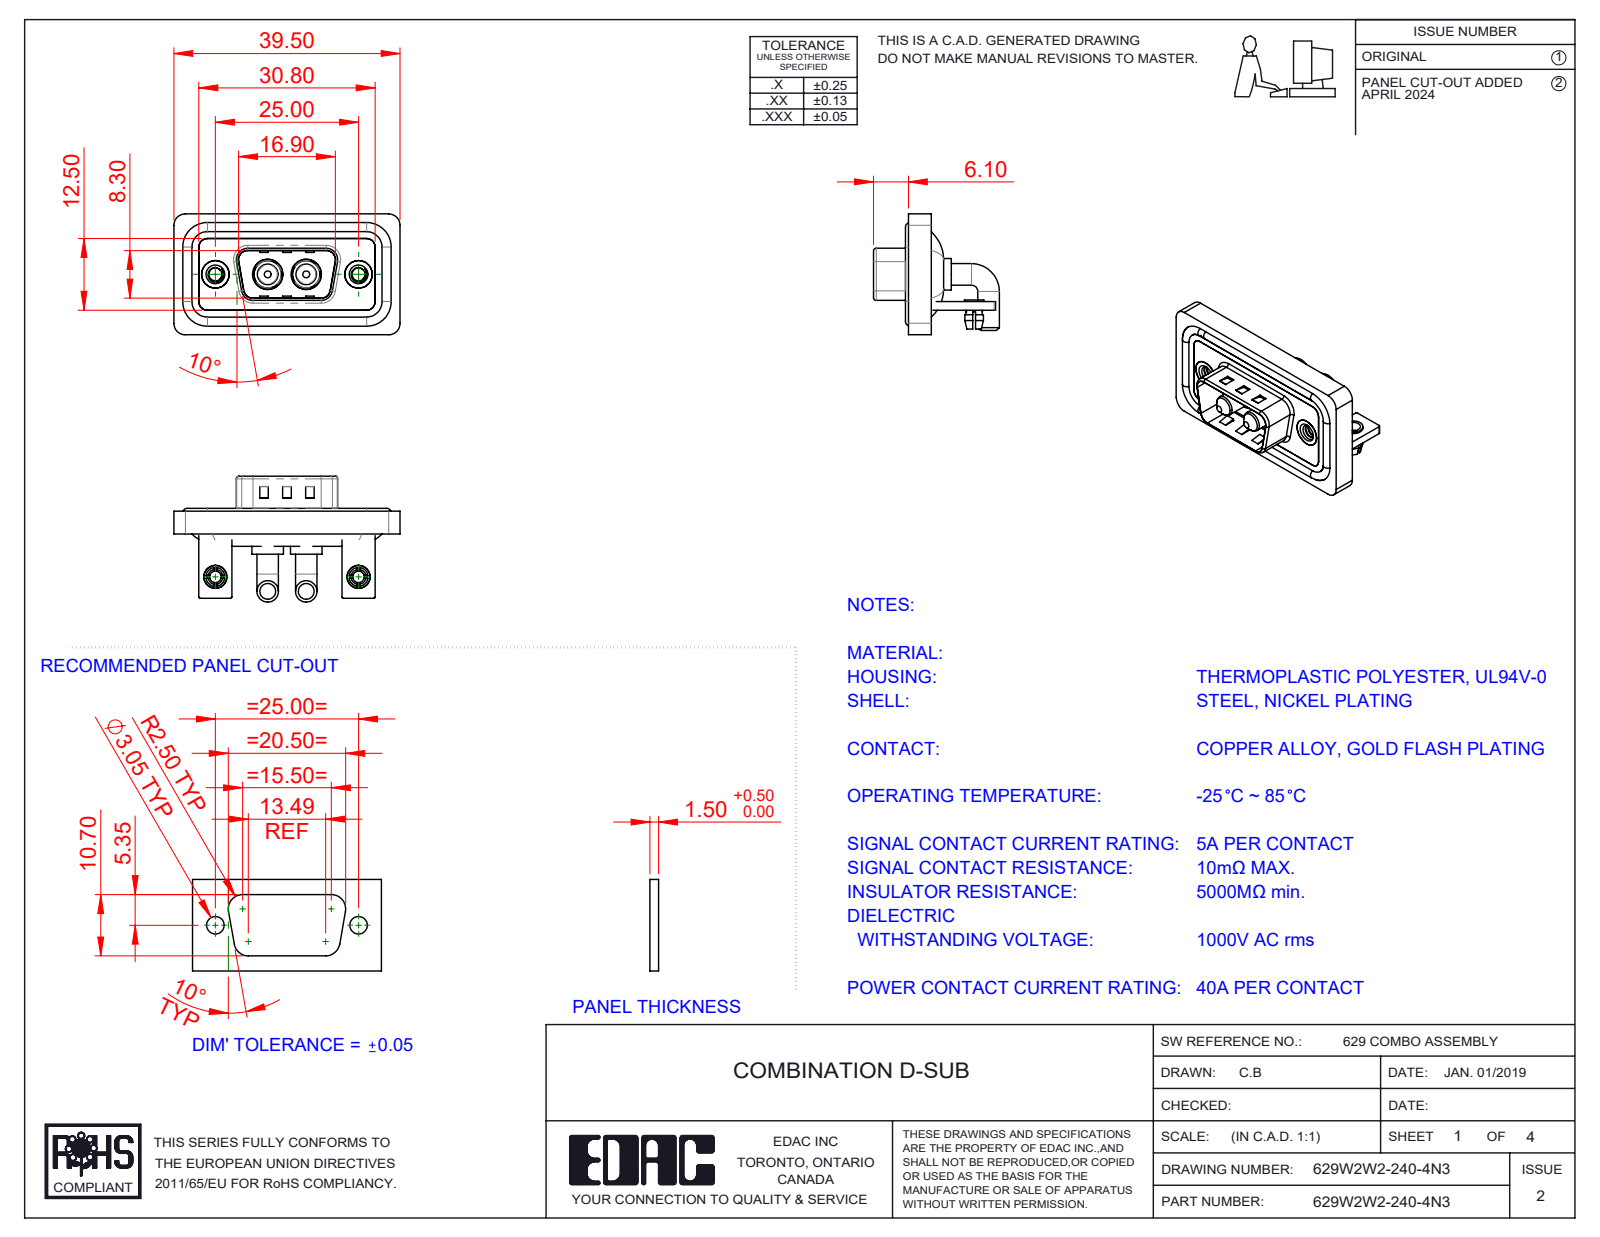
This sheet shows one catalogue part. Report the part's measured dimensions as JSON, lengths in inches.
{"part_name": "629Combo Waterproof Housing_09 Contacts; 629Combo Board Lock; 629Combo Shell Front_09 Contacts; 629Combo Threaded Rivet_3 (+5 more)", "step_written_by": "SolidWorks 2023 (CONFIG_CONTROL_DESIGN)", "units": "inches", "bodies": {"solids": 15, "faces": 629, "planar": 233, "cylindrical": 272, "other": 124}, "overall_size": [1.555, 0.865, 0.831], "volume_in3": 0.308, "surface_area_in2": 12.48, "round_holes": [[0.079, 2], [0.089, 2], [0.098, 2], [0.126, 2], [0.157, 2], [0.189, 2], [0.191, 2], [0.197, 2], [0.209, 2]], "round_bosses_or_shafts": [[0.148, 4], [0.063, 4], [0.217, 2], [0.205, 2], [0.193, 2], [0.187, 2], [0.157, 2], [0.142, 2]], "partial_cylinders_radius": [[0.079, 19], [0.059, 18], [0.01, 16], [0.02, 9], [0.063, 8], [0.024, 4], [0.026, 4], [0.035, 4]], "face_to_face_distances": [0.016, 0.059, 0.114, 0.031, 0.043, 0.047, 0.083, 0.063, 0.146, 0.098], "hole_center_spacings": [0.36, 0.624, 0.984, 0.265]}
